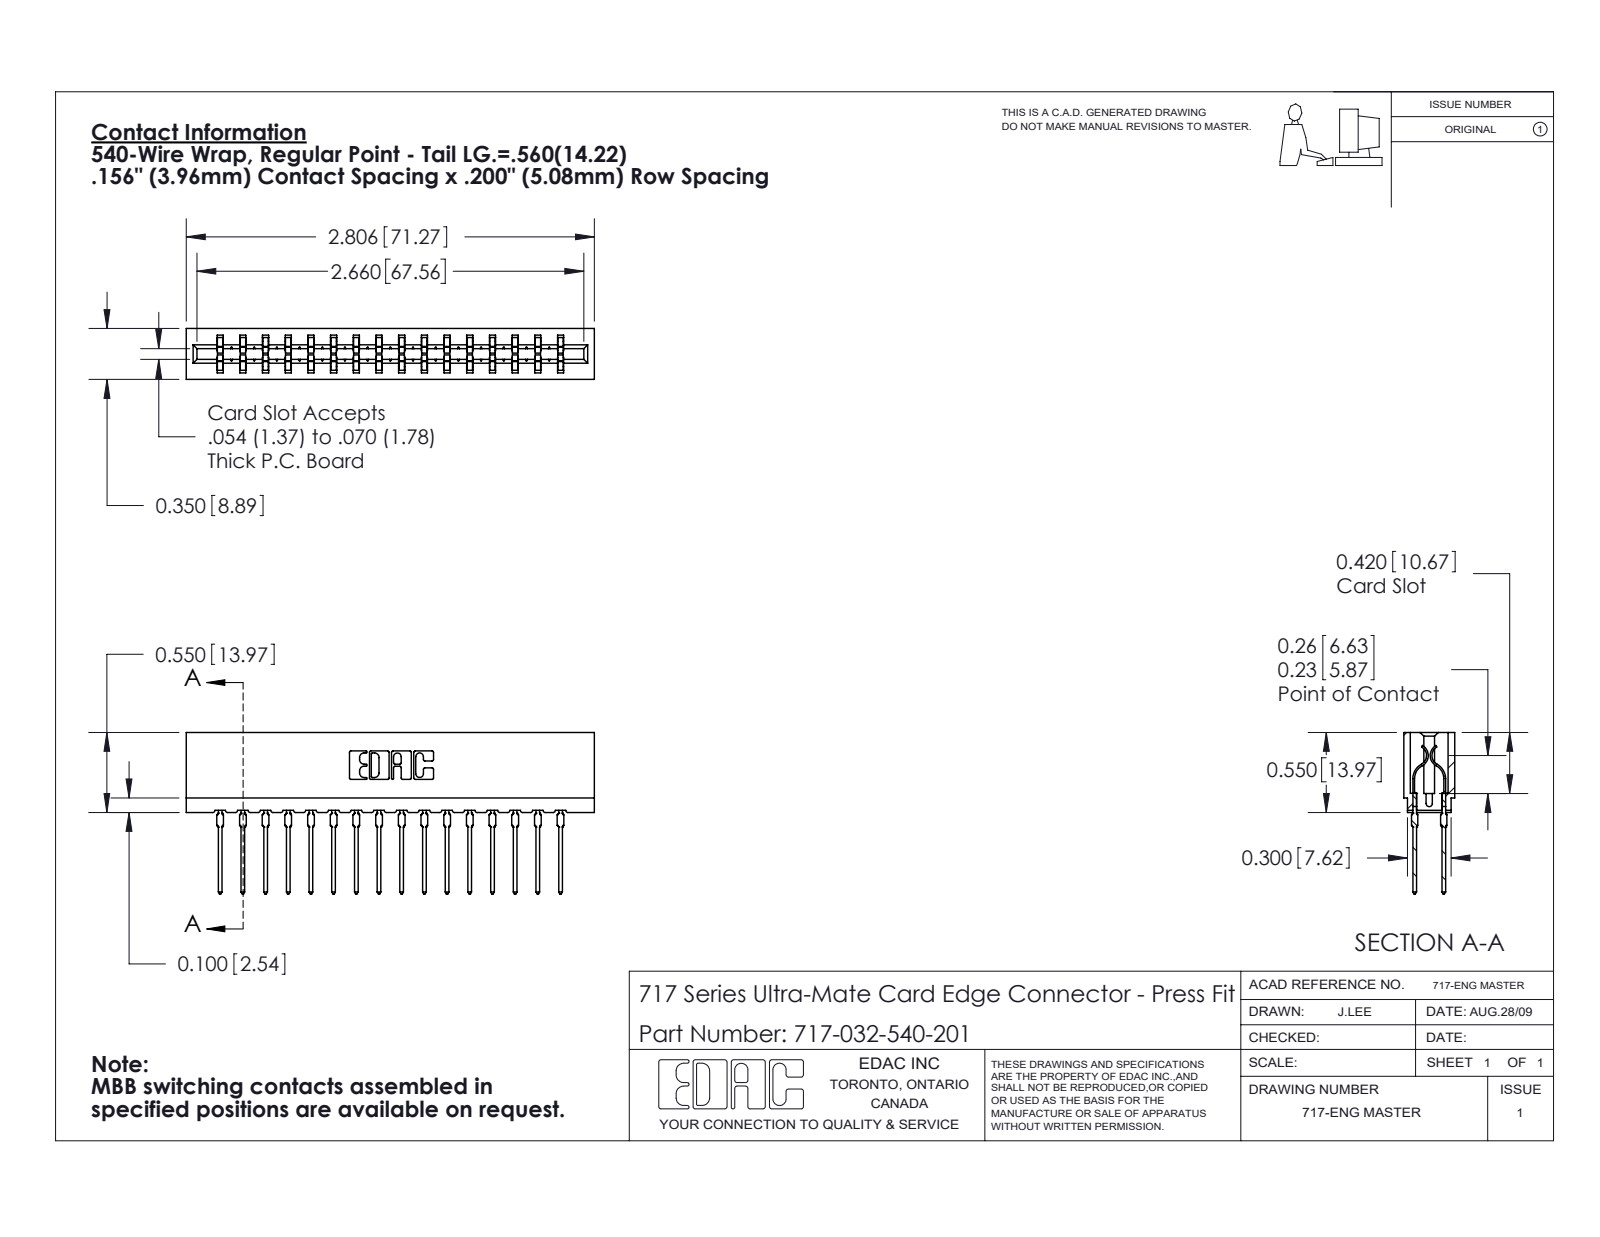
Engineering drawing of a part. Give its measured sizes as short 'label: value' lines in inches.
name: 717-032-540-201; 717 Part_Insulator Option - 06; 745-292-001_540
written by: SolidWorks 2020 (CONFIG_CONTROL_DESIGN)
unit: in
bodies: 33 solids, 2974 faces (1542 planar, 600 cylindrical, 832 other)
size: 2.806 × 1.109 × 0.35
volume: 0.389 in³; area: 15.23 in²
rounds: 64× R0.021, 32× R0.015, 22× R0.01, 8× R0.005, 8× R0.011, 6× R0.007, 6× R0.031, 3× R0.026
face distances: 0.212, 0.138, 0.35, 0.156, 0.063, 0.287, 0.076, 0.149, 0.468, 0.624
